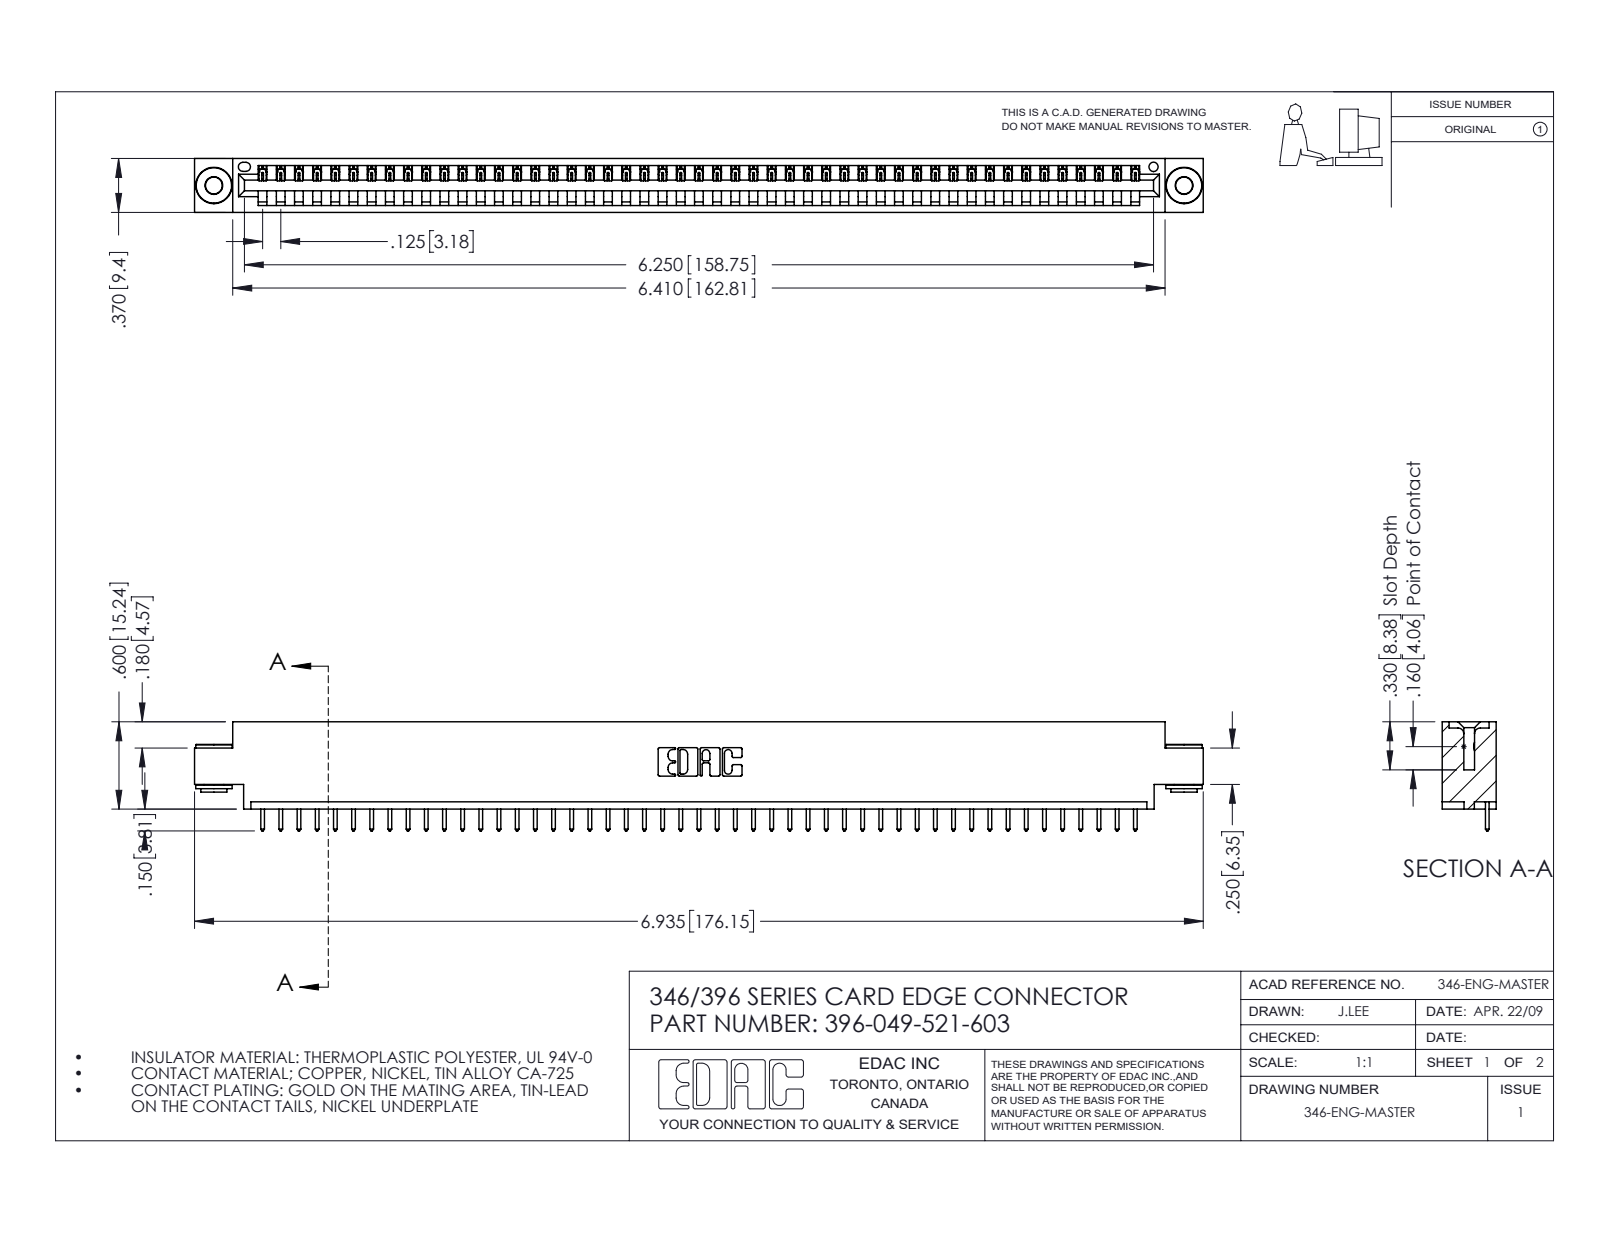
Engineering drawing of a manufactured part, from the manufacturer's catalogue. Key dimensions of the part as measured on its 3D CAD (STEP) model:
Part name (STEP PRODUCT): 345-292-001_345-293-121; 345-250-002_345-250-002-102; 346 Part_0.170 Offset - 0.156 Dia-TH; 396-049-521-603
STEP written by: SolidWorks 2016 (CONFIG_CONTROL_DESIGN)
Units: inches
Bodies: 52 solids, 3006 faces (2050 planar, 948 cylindrical, 8 other)
Overall size (bounding box): 6.935 × 0.75 × 0.37
Volume: 1.015 in³ · Surface area: 32.07 in²
Round holes (diameter × count): ⌀0.116 ×2, ⌀0.156 ×2, ⌀0.064 ×1
Round bosses / shafts (diameter × count): ⌀0.25 ×2, ⌀0.18 ×2, ⌀0.136 ×2
Partial cylindrical surfaces — rounded edges, fillets, slot ends (radius × count): R0.006 ×98, R0.01 ×98, R0.01 ×22, R0.007 ×6, R0.031 ×6, R0.026 ×3, R0.031 ×2, R0.04 ×2
Main face-to-face distances: 0.048, 0.322, 0.37, 0.25, 0.025, 0.072, 0.298, 0.148, 0.222, 0.1
Hole centre spacings: 0.246, 6.461, 6.67
